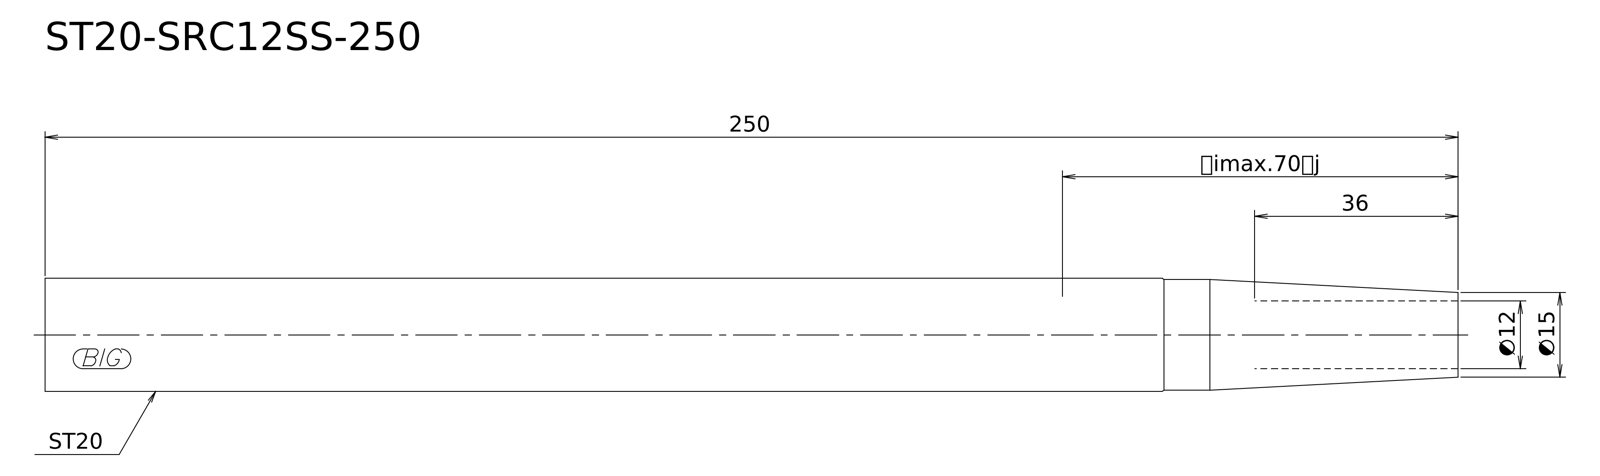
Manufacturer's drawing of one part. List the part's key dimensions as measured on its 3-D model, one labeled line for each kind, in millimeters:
STEP written by: Kubotek KeyCreator V8.5.1 (14335) (CONFIG_CONTROL_DESIGN)
Units: millimetres
Bodies: 1 solid, 6 faces (2 planar, 2 cylindrical, 2 other)
Overall size (bounding box): 250 × 20 × 20
Volume: 75 026 mm³ · Surface area: 15 823 mm²
Round bosses / shafts (diameter × count): ⌀20 ×1, ⌀19.6 ×1
Main face-to-face distances: 250
